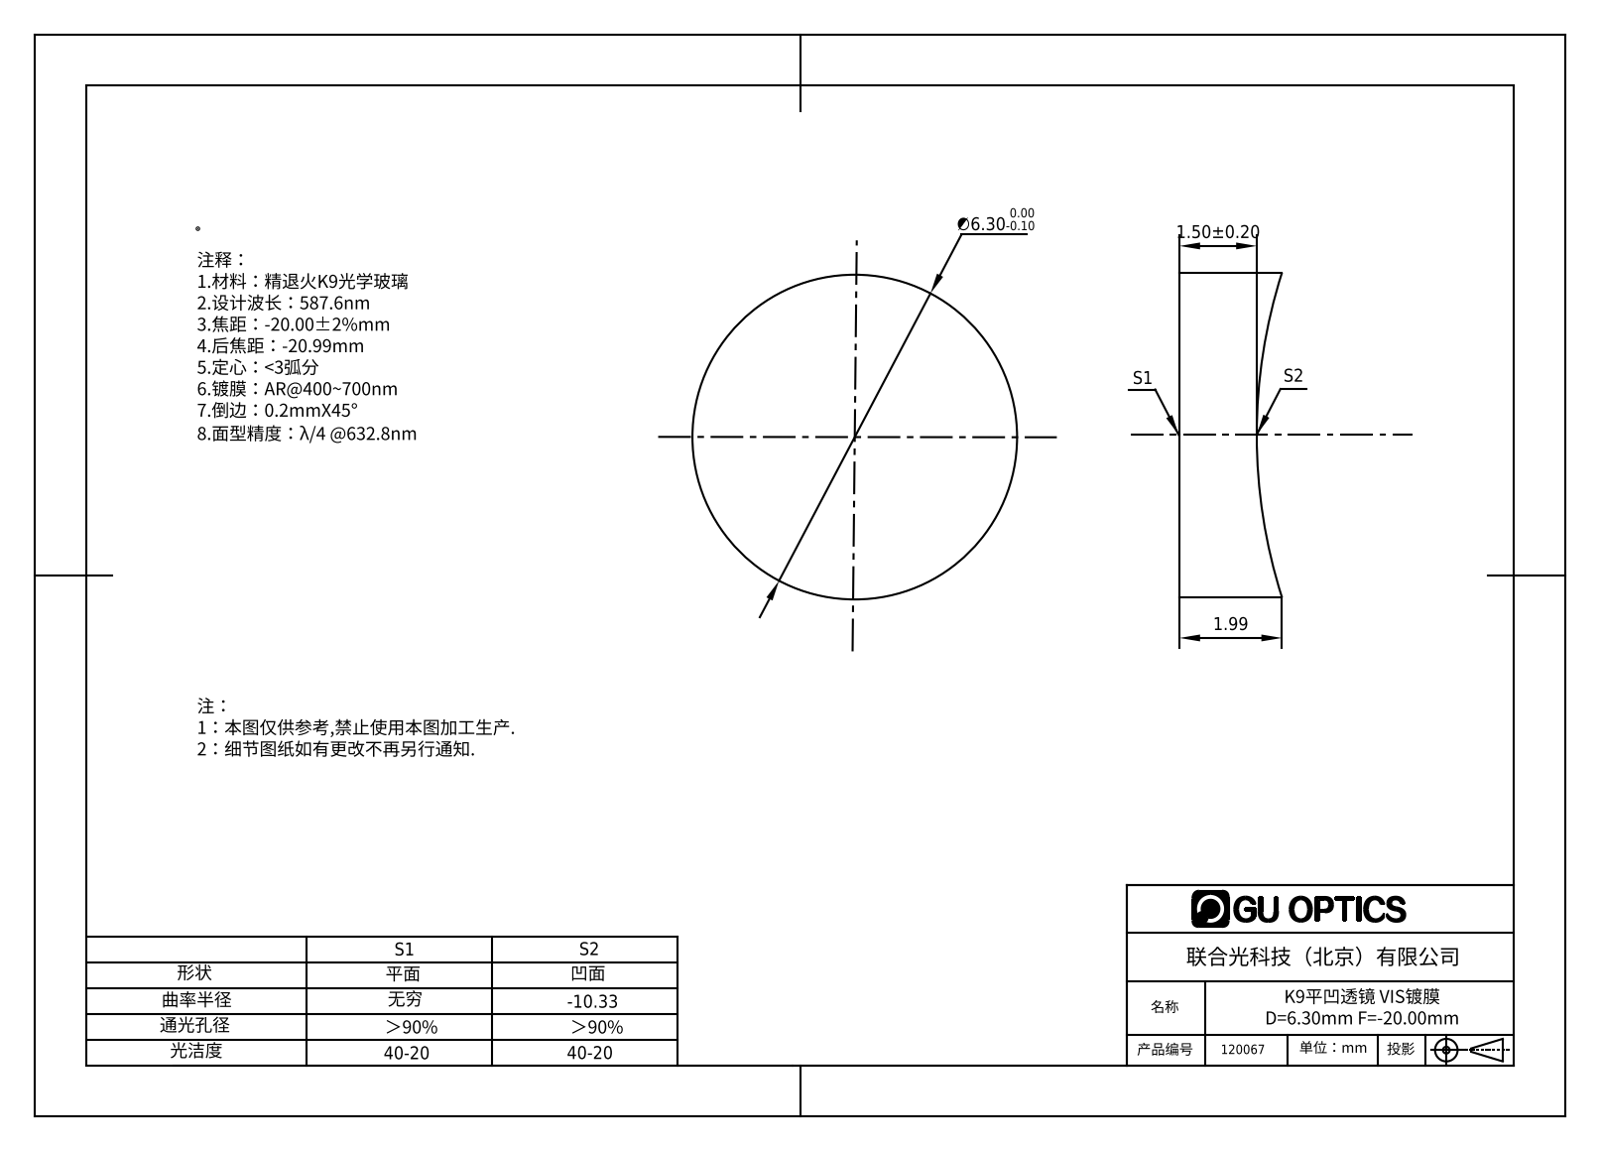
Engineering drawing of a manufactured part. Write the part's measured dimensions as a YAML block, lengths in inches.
part_name: "120007"
step_written_by: "SolidWorks 2016 (AUTOMOTIVE_DESIGN)"
units: inches
bodies: {solids: 1, faces: 5, planar: 1, cylindrical: 2, other: 2}
overall_size: [0.248, 0.248, 0.078]
volume: 0.003
surface_area: 0.158
round_bosses_or_shafts:
  - {diameter: 0.248, count: 1}
